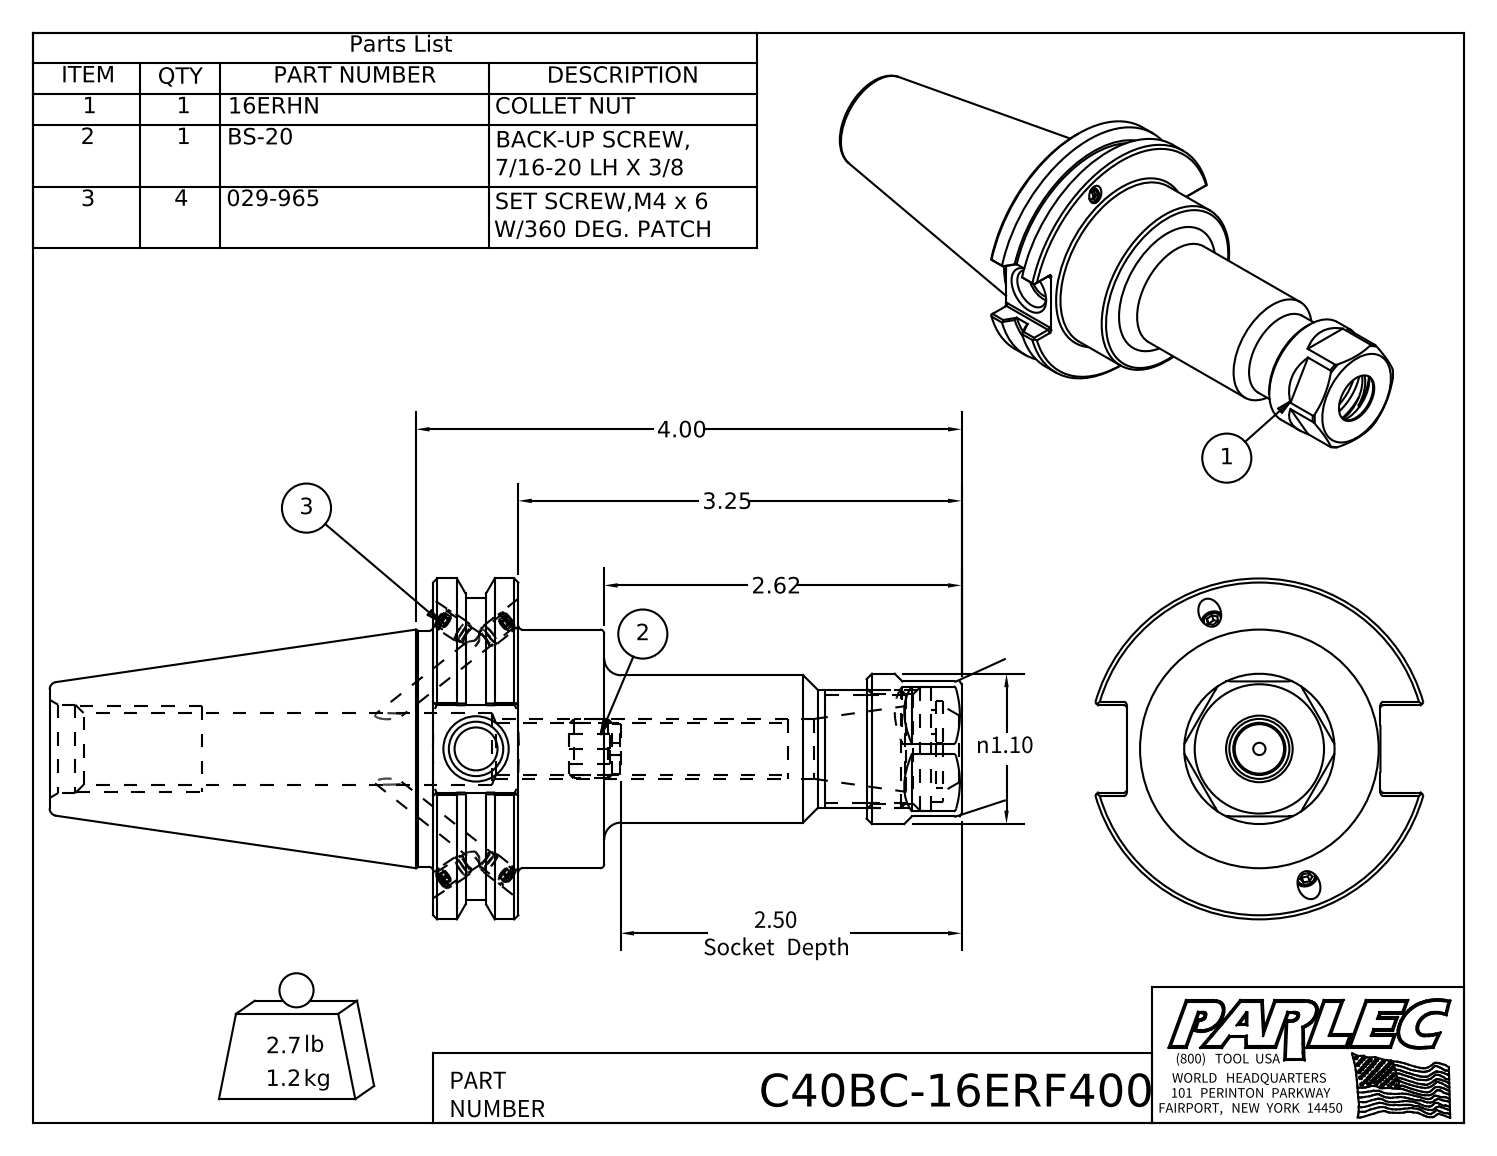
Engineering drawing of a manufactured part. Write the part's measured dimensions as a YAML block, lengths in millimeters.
part_name: "C40BCB-16ER4-1; 029-965; 16ERHN; BS-20 (+1 more)"
step_written_by: "Autodesk Inventor 2016 (AUTOMOTIVE_DESIGN)"
units: millimeters
bodies: {solids: 7, faces: 223, planar: 103, cylindrical: 58, other: 62}
overall_size: [169.85, 63.5, 61.11]
volume: 153338
surface_area: 34382
round_holes:
  - {diameter: 3.3, count: 4}
  - {diameter: 4.1, count: 4}
  - {diameter: 2.29, count: 1}
  - {diameter: 8, count: 1}
  - {diameter: 9.73, count: 1}
  - {diameter: 10.13, count: 1}
  - {diameter: 11.18, count: 1}
  - {diameter: 12.4, count: 1}
  - {diameter: 13.39, count: 1}
  - {diameter: 16.46, count: 1}
  - {diameter: 17.02, count: 1}
  - {diameter: 20.5, count: 1}
round_bosses_or_shafts:
  - {diameter: 4.2, count: 4}
  - {diameter: 4, count: 4}
  - {diameter: 63.5, count: 1}
  - {diameter: 56.36, count: 1}
  - {diameter: 44.45, count: 1}
  - {diameter: 43.94, count: 1}
  - {diameter: 28, count: 1}
  - {diameter: 27.43, count: 1}
partial_cylinders:
  - {radius: 0.51, count: 12}
  - {radius: 7.24, count: 1}
  - {radius: 9, count: 1}
face_to_face_distances: [15.87, 31.88, 16.01, 66.54, 98.42, 82.55, 25.14, 4.44, 20.7, 92.72]
hole_center_spacings: [1.52]
